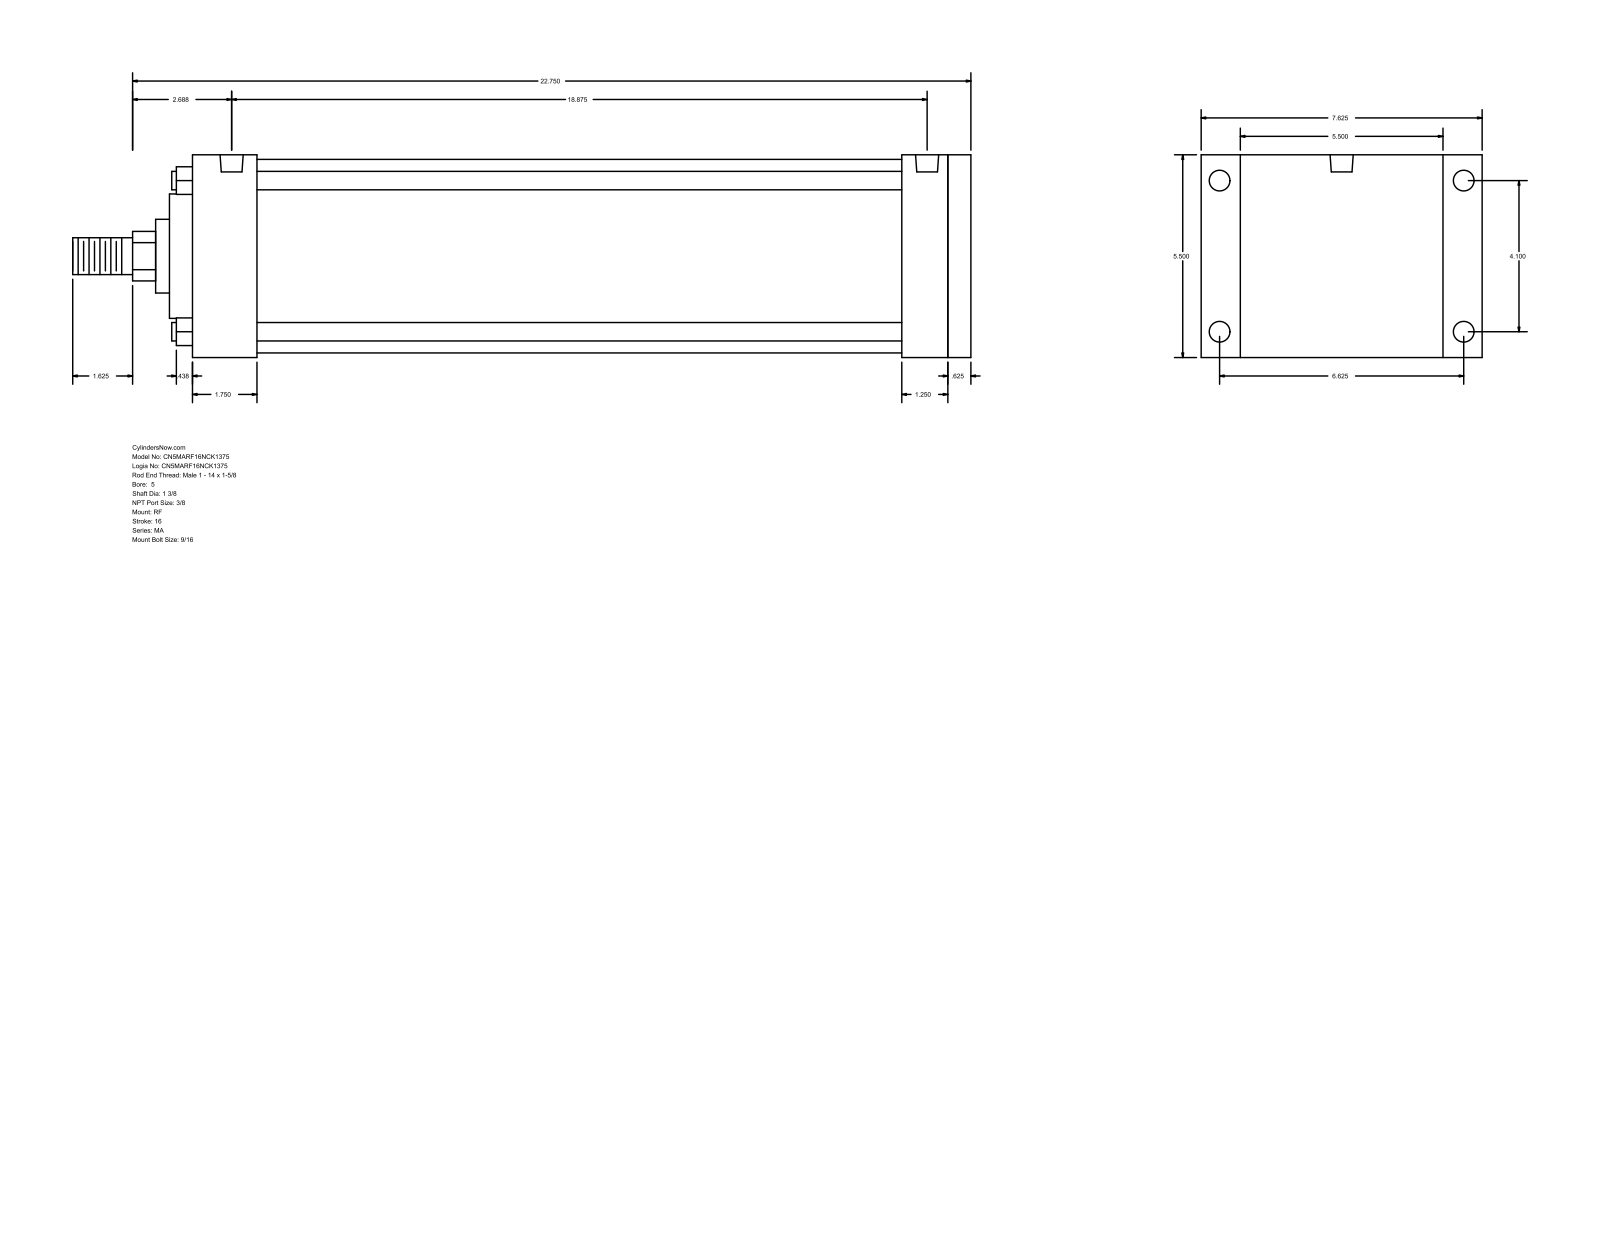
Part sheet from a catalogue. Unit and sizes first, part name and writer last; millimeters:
Units: millimetres
Overall size (bounding box): 619.12 × 193.68 × 139.7
Round holes (diameter × count): ⌀11.11 ×4, ⌀14.29 ×4, ⌀15.93 ×2
Round bosses / shafts (diameter × count): ⌀12.7 ×4, ⌀133.35 ×1, ⌀85.72 ×1, ⌀50.8 ×1, ⌀34.92 ×1, ⌀25.4 ×1
Partial cylindrical surfaces — rounded edges, fillets, slot ends (radius × count): R17.06 ×1
Main face-to-face distances: 139.7, 536.58, 15.87, 520.71, 44.45, 476.26, 492.13, 488.96, 444.51, 31.75
Hole centre spacings: 4.77, 104.14, 168.28, 197.9, 469.89, 474.66, 479.43
Bodies: 0 solids, 94 faces (65 planar, 29 cylindrical, 0 other)
Part name (STEP PRODUCT): MA_RF__0500_1.375
STEP written by: GSSL Pune (CONFIG_CONTROL_DESIGN)
